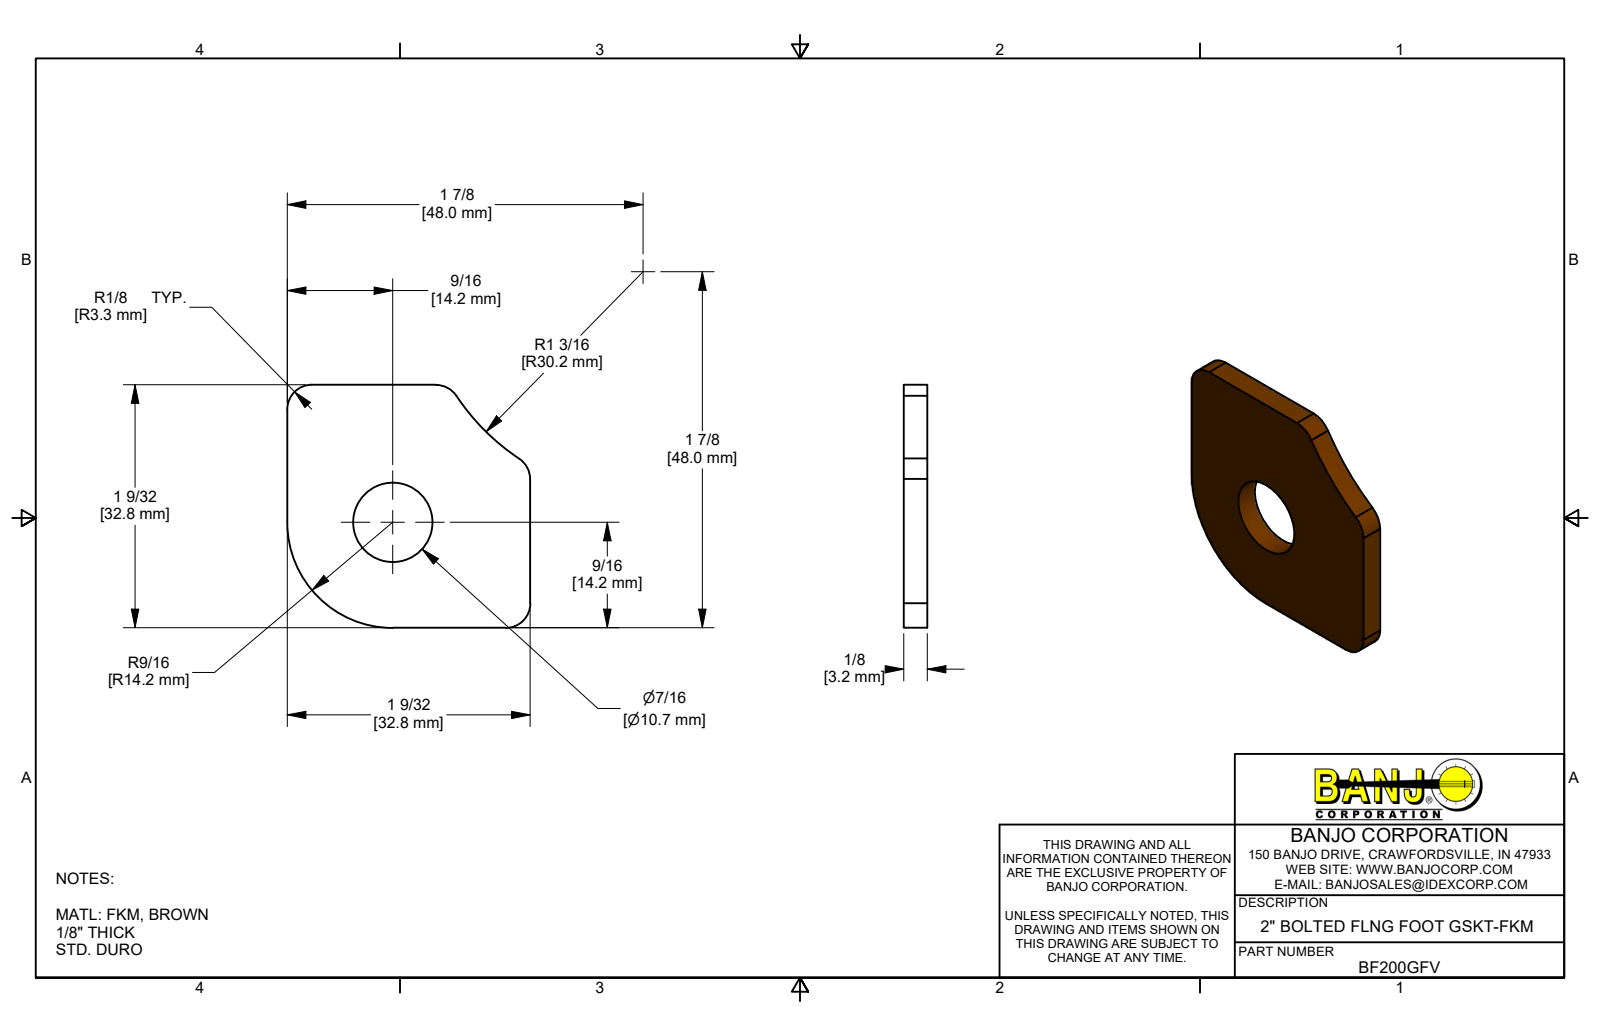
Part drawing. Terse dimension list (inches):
name: BF200GFV
written by: Autodesk Inventor 2019 (AUTOMOTIVE_DESIGN)
unit: in
bodies: 1 solid, 13 faces (6 planar, 7 cylindrical, 0 other)
size: 1.29 × 1.29 × 0.125
volume: 0.168 in³; area: 3.415 in²
holes: 1× ⌀0.422
rounds: 4× R0.13, 1× R0.56, 1× R1.19
face distances: 0.125, 1.29
